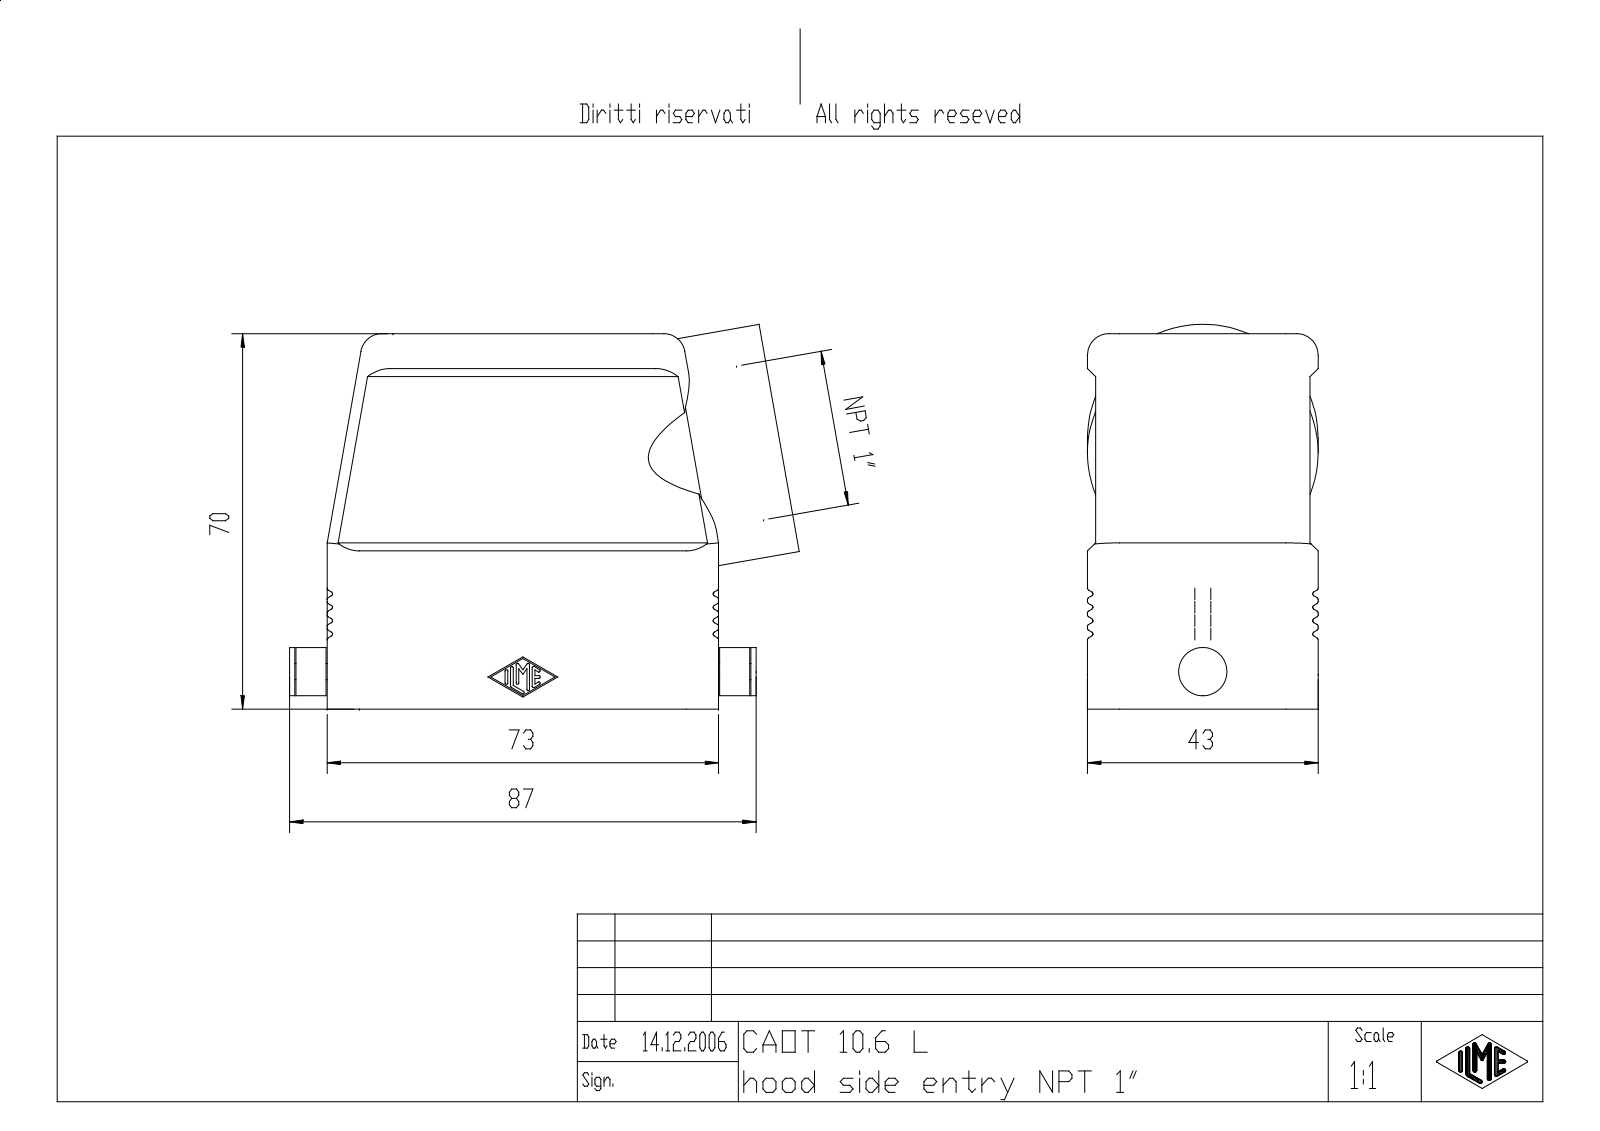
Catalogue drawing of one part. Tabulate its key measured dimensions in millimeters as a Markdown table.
| quantity | value |
| --- | --- |
| part name | MSBO11097 |
| STEP written by | Creo Elements/Direct Modeling 18.0B 02-Dec-2011 (C) Parametric Technology GmbH (AUTOMOTIVE_DESIGN) |
| units | millimeters |
| bodies | 1 solid, 523 faces (198 planar, 213 cylindrical, 112 other) |
| overall size | 95.02 × 71.74 × 43 |
| volume | 64 643 mm³ |
| surface area | 40 408 mm² |
| round holes (diameter × count) | 2.46 × 4, 3.1 × 4 |
| round bosses / shafts (diameter × count) | 43 × 1, 9 × 1, 3 × 1 |
| partial cylindrical surfaces (radius × count) | 0.4 × 64, 0.25 × 14, 3 × 10, 6 × 10, 2 × 4, 4 × 4, 5 × 4 |
| main face-to-face distances | 1.5, 3, 40, 38.5, 37, 41.5, 8.5, 11.5, 70, 58.5 |
| hole center spacings | 27, 57, 63.07 |
